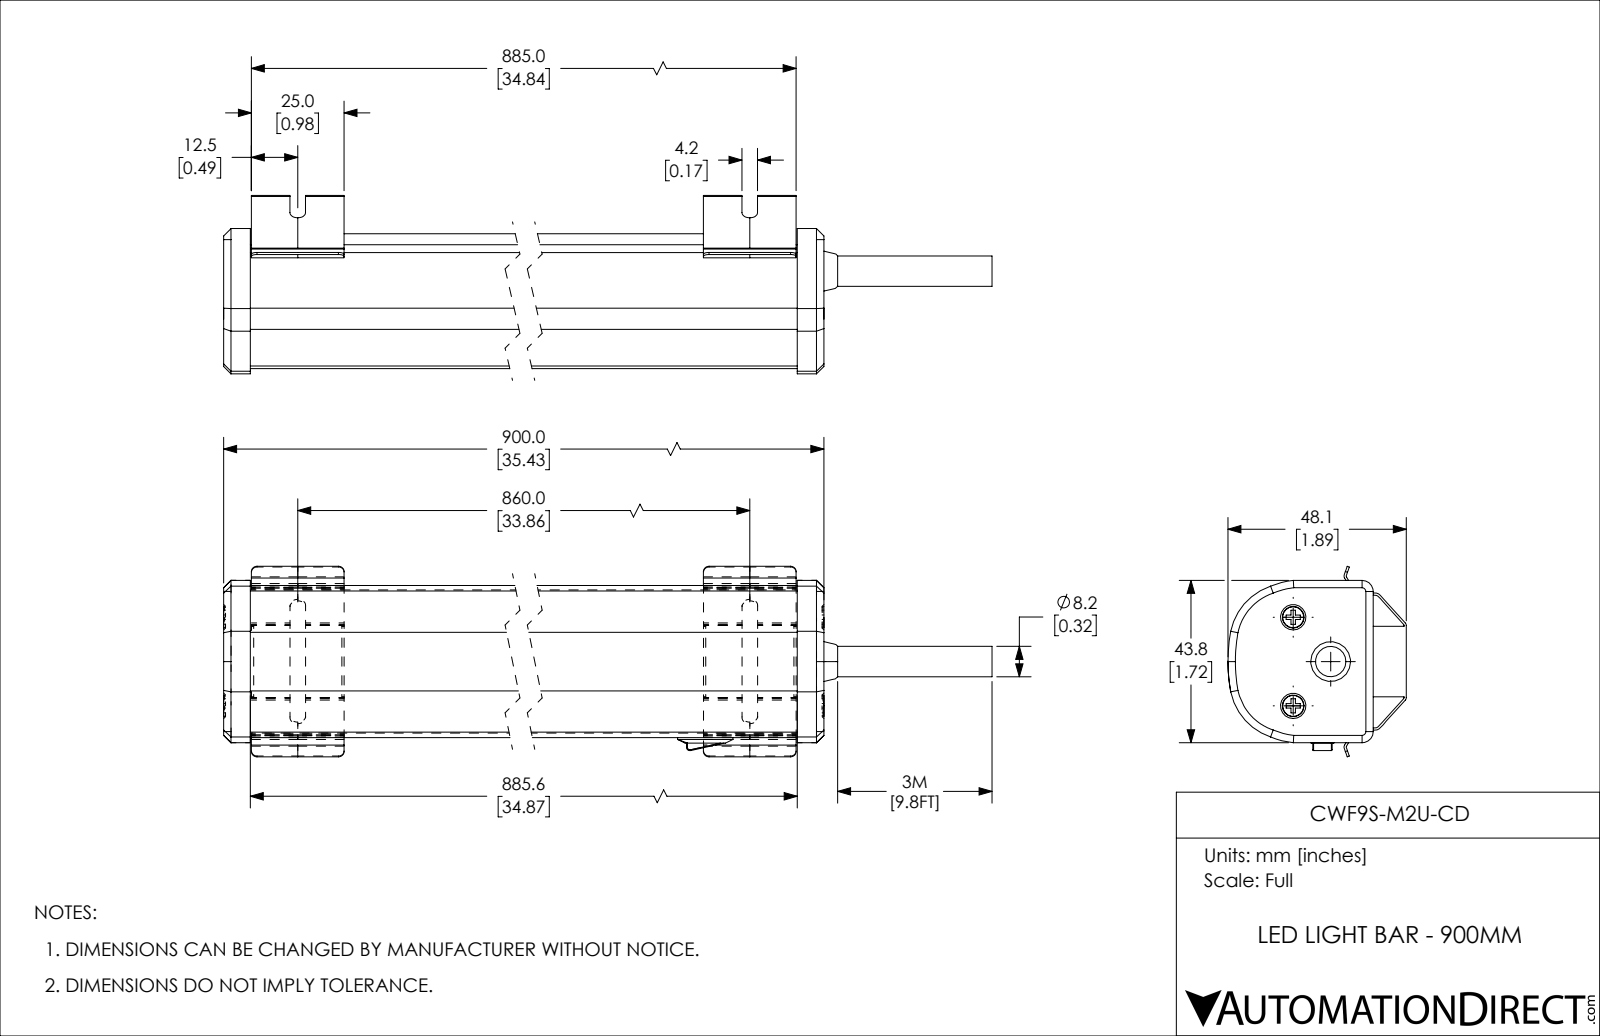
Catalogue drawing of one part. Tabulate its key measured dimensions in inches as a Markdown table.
| quantity | value |
| --- | --- |
| part name | CWF9S-M2U-CD |
| STEP written by | SolidWorks 2018 (AUTOMOTIVE_DESIGN) |
| units | inches |
| bodies | 3 solids, 283 faces (123 planar, 67 cylindrical, 93 other) |
| overall size | 37.22 × 2.023 × 1.894 |
| volume | 74.76 in³ |
| surface area | 219.8 in² |
| round bosses / shafts (diameter × count) | 0.224 × 2, 0.323 × 1 |
| partial cylindrical surfaces (radius × count) | 0.059 × 8, 0.083 × 4, 0.006 × 2, 0.008 × 2, 0.016 × 2, 0.03 × 2, 0.039 × 2, 0.591 × 2 |
| main face-to-face distances | 1.614, 0.047, 1.567, 0.083, 1.52, 0.024, 35.433, 33.858, 0.606, 0.523 |
